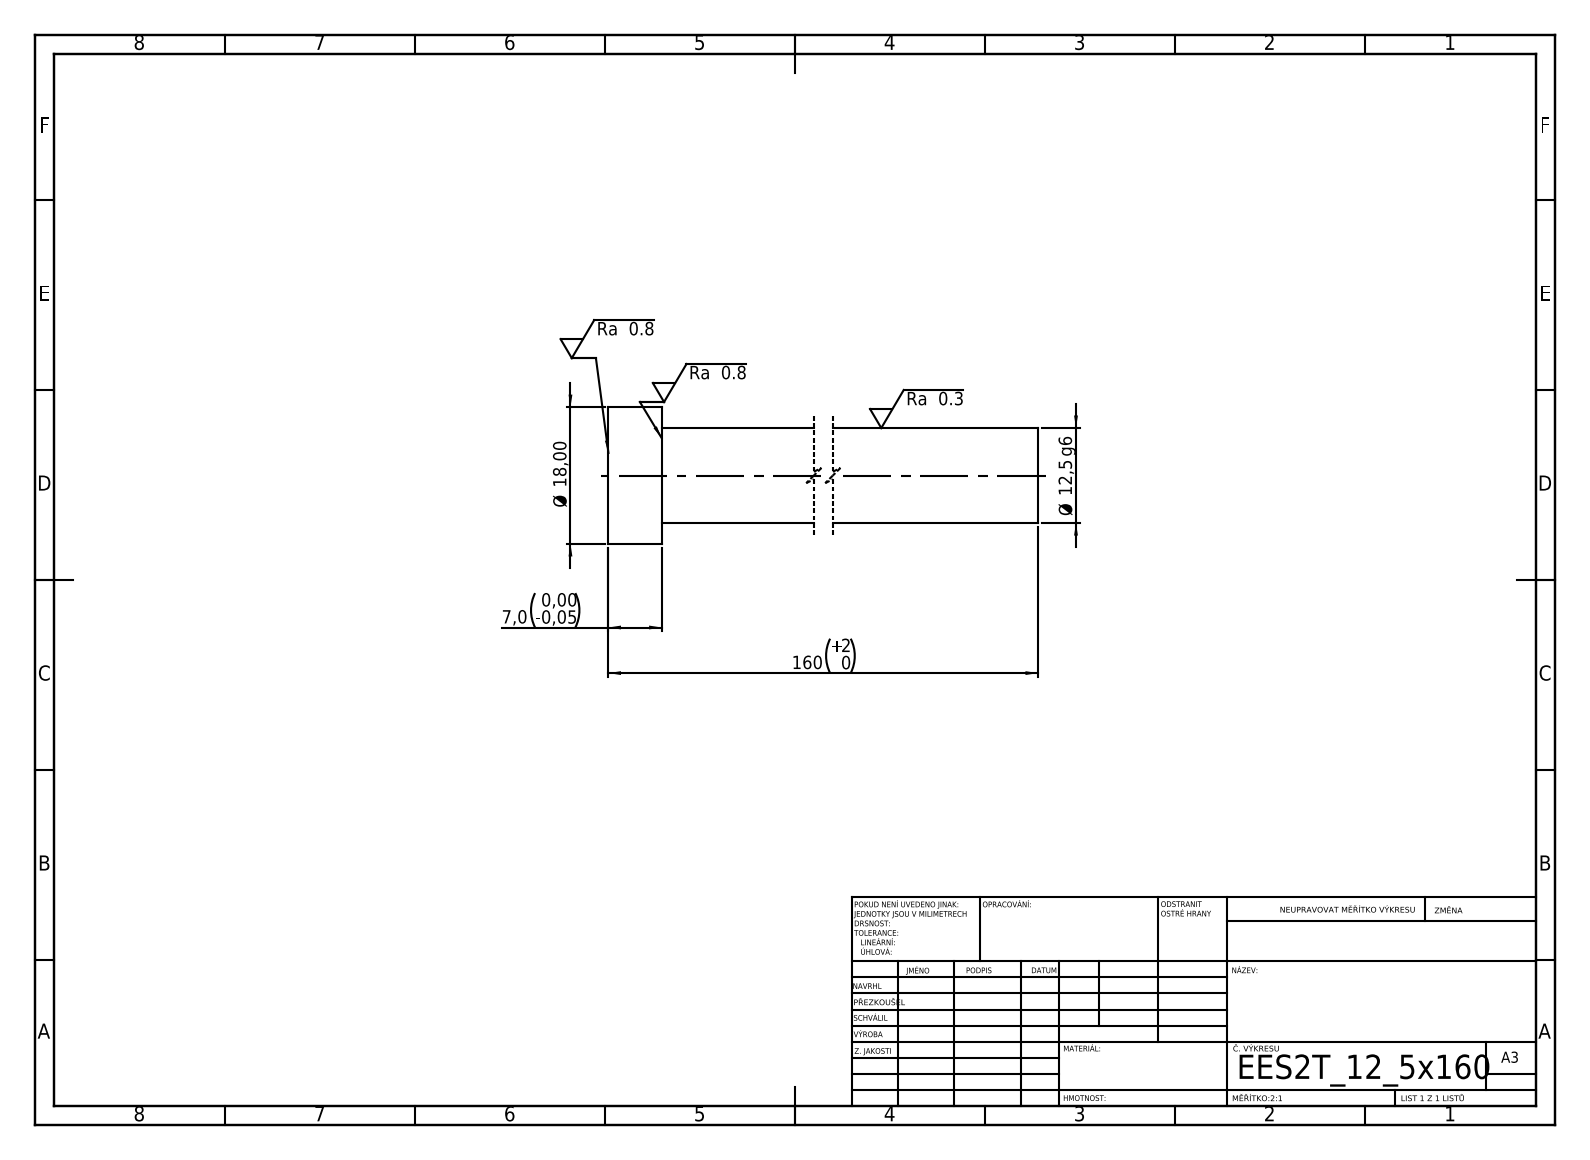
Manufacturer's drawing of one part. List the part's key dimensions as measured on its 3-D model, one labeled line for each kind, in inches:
STEP written by: SolidWorks 2019 (CONFIG_CONTROL_DESIGN)
Units: inches
Bodies: 1 solid, 7 faces (3 planar, 4 cylindrical, 0 other)
Overall size (bounding box): 6.299 × 0.709 × 0.709
Volume: 1.254 in³ · Surface area: 10.72 in²
Round bosses / shafts (diameter × count): ⌀0.709 ×1, ⌀0.492 ×1
Main face-to-face distances: 0.276, 6.299, 6.024
